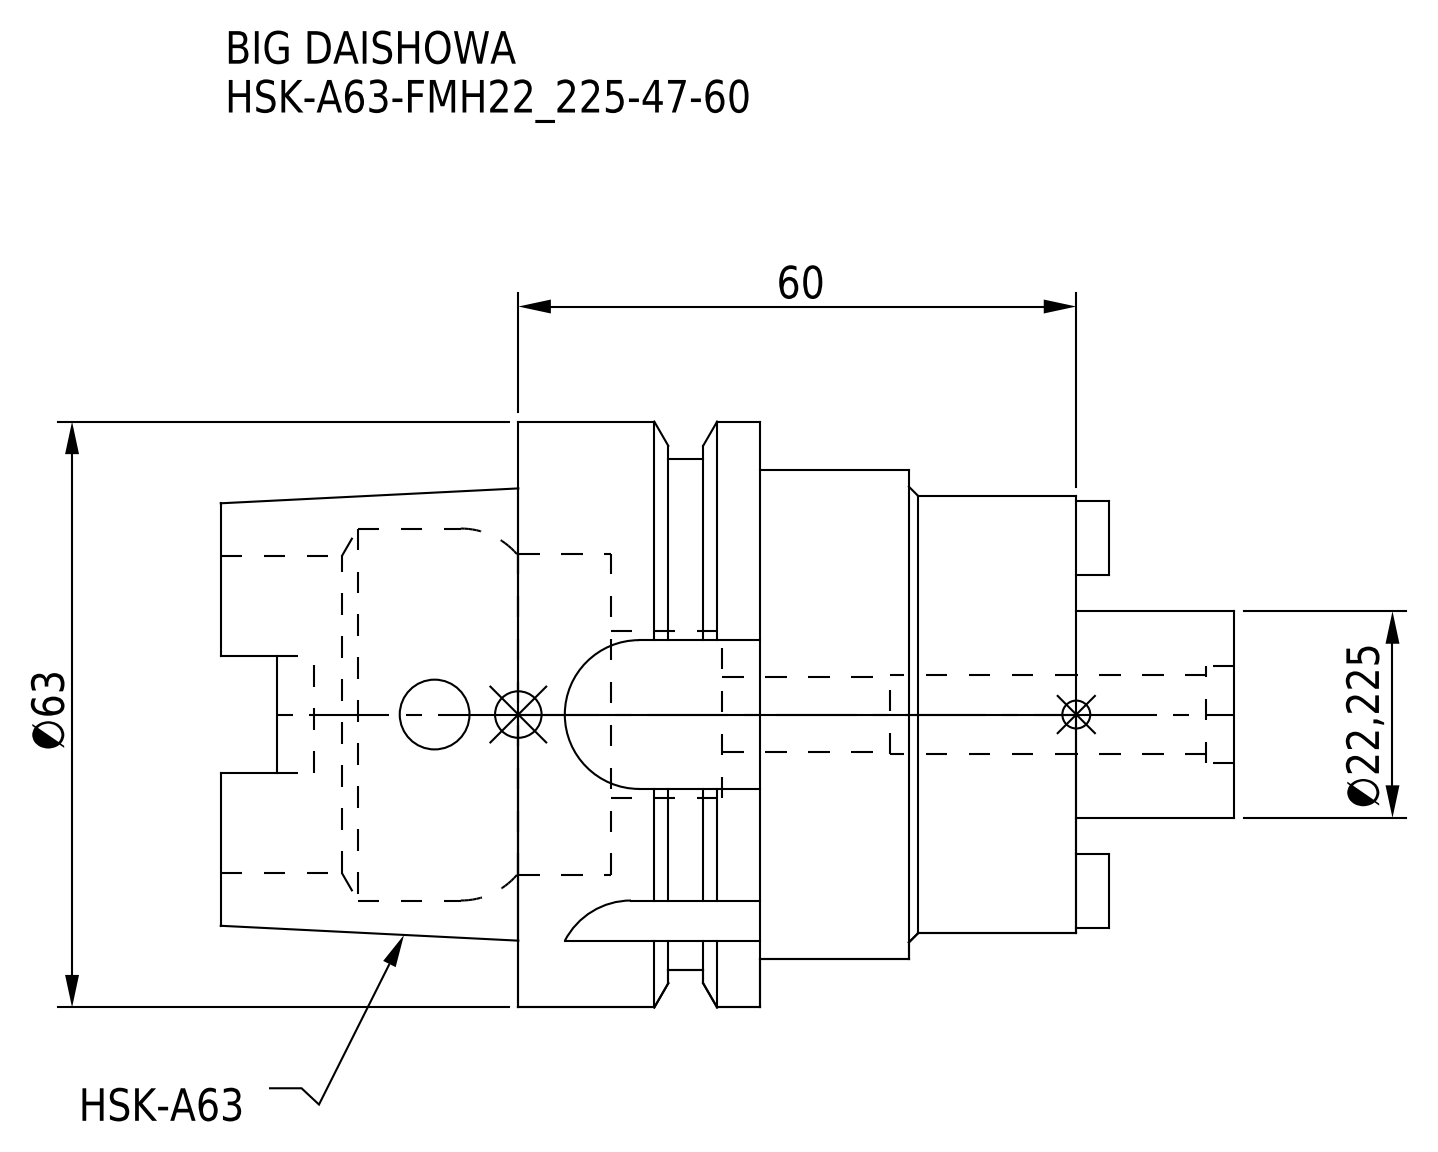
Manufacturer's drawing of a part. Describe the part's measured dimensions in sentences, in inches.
The part is named "HSK-A63-FMH22_225-47-60". Its 3-D file was written by "CREO PARAMETRIC BY PTC INC, 2016380 (AUTOMOTIVE_DESIGN)". It is 1 solid with 97 faces: 45 planar, 38 cylindrical and 14 other. Overall it measures 4.291 by 2.48 by 2.48 inches. Its volume is 9.277 cubic inches and its surface area 47.17 square inches. Round holes: 1 of diameter 0.295, 1 of diameter 0.315, 1 of diameter 0.335, 1 of diameter 0.413, 1 of diameter 0.709, 1 of diameter 1.339, 1 of diameter 1.358, 1 of diameter 1.575. Round bosses or shafts: 1 of diameter 2.48, 1 of diameter 2.165, 1 of diameter 2.071, 1 of diameter 1.85, 1 of diameter 0.875. Partial cylindrical surfaces (rounded edges, fillets, slot ends): 2 of radius 0.315, 1 of radius 0.354. The main face-to-face distances are 2.362, 1.024, 1.339, 1.97, 0.632, 0.392, 1.26, 3.622, 2.283, 1.652.
